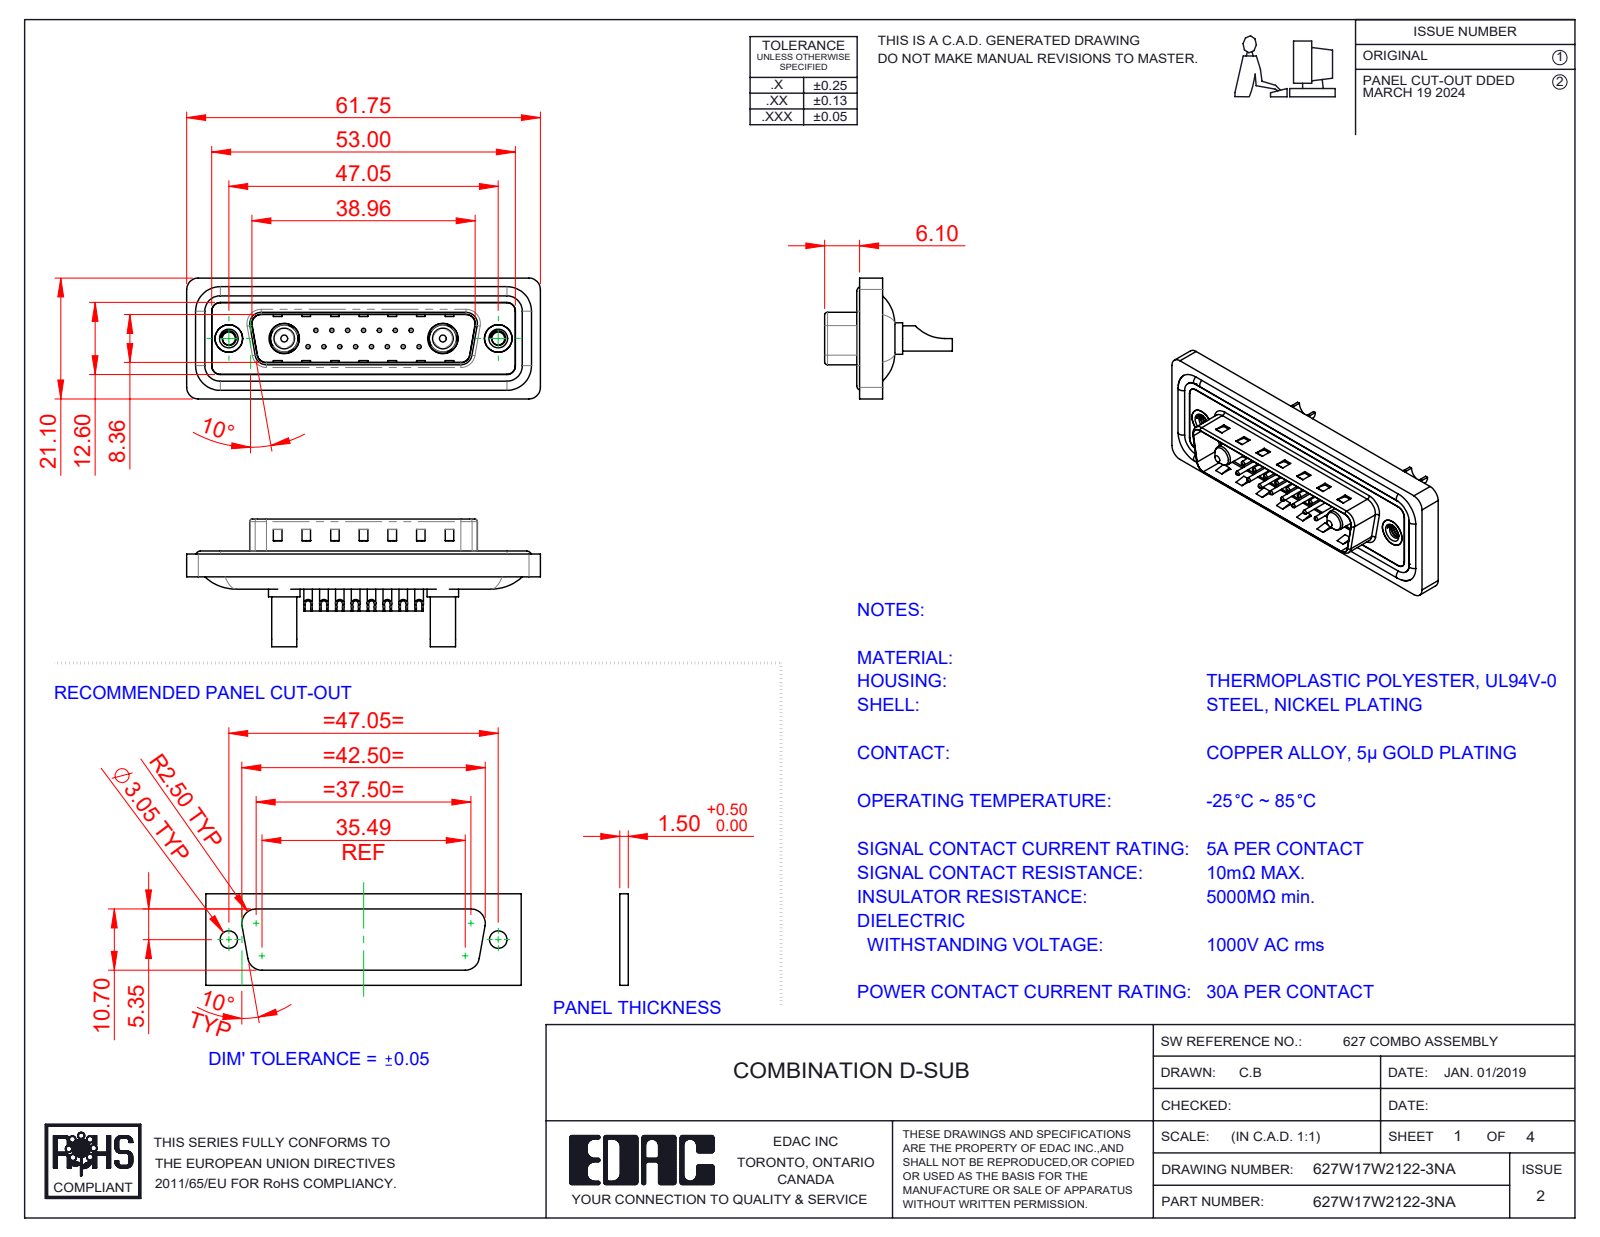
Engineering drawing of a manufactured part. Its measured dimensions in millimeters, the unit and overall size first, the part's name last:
Units: millimetres
Overall size (bounding box): 61.75 × 22.3 × 21.1
Round holes (diameter × count): ⌀0.75 ×15, ⌀1 ×15, ⌀1.6 ×15, ⌀2 ×15, ⌀2.26 ×2, ⌀3.5 ×2, ⌀4 ×2, ⌀4.8 ×2, ⌀4.85 ×2, ⌀5 ×2, ⌀5.3 ×2
Round bosses / shafts (diameter × count): ⌀1.5 ×15, ⌀1.6 ×4, ⌀5.5 ×2, ⌀5.2 ×2, ⌀4.9 ×2, ⌀4.75 ×2, ⌀4.4 ×2, ⌀3.75 ×2
Partial cylindrical surfaces — rounded edges, fillets, slot ends (radius × count): R1.5 ×22, R2 ×18, R0.5 ×8, R1.6 ×8, R1 ×6, R0.25 ×4, R0.6 ×4, R0.65 ×4
Main face-to-face distances: 0.4, 1.5, 1.1, 1.6, 0.5, 3.1, 2.9, 0.82, 9.58, 4.1
Hole centre spacings: 3.16, 2.77, 5.54, 8.31, 5.04, 7.49, 11.08, 5.03
Volume: 7 339 mm³ · Surface area: 12 246 mm²
Bodies: 26 solids, 1126 faces (370 planar, 474 cylindrical, 282 other)
Part name (STEP PRODUCT): Power Pin_30A SC; 627Combo Housing_17W2; 627Combo Shell Rear_25 Contacts; 627Combo Shell Front_25 Contacts (+5 more)
STEP written by: SolidWorks 2023 (CONFIG_CONTROL_DESIGN)
